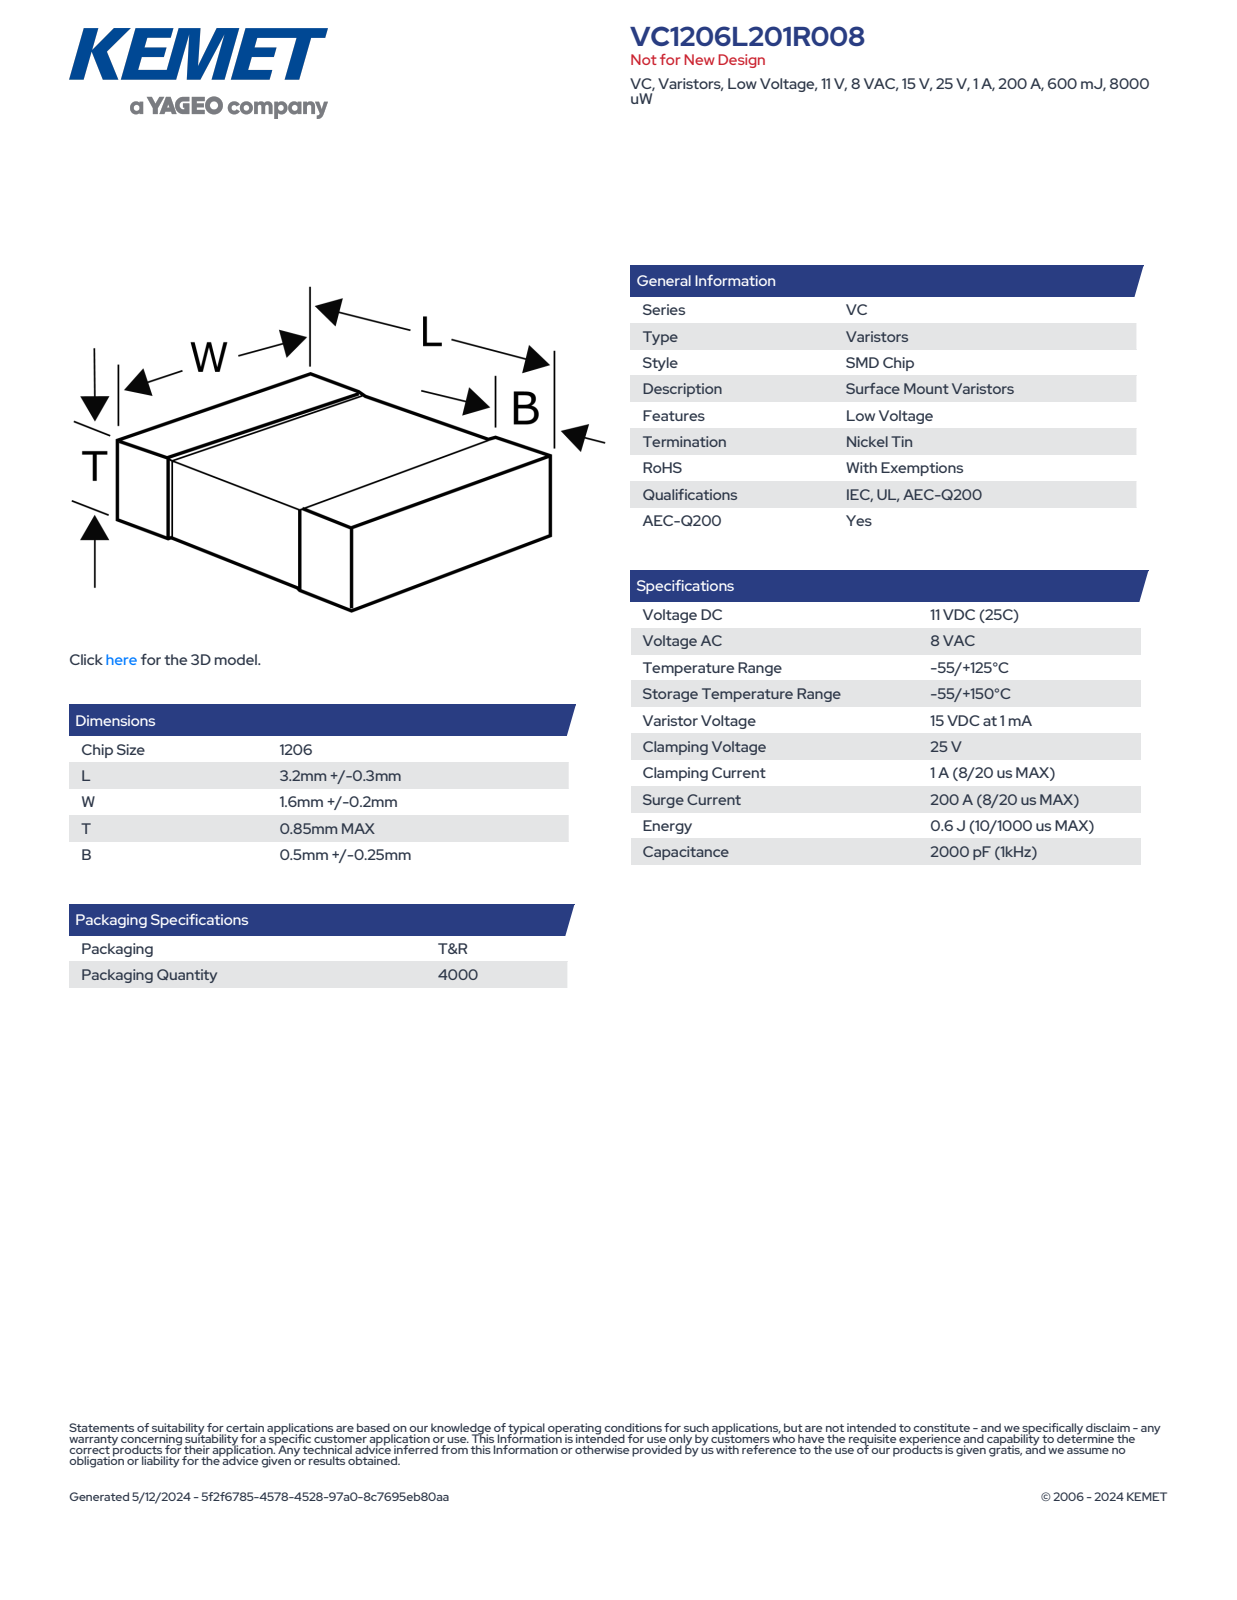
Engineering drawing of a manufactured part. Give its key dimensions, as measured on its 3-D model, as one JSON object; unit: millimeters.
{"part_name": "VS_SMD_1206_L3.50W1.8T0.85B0.75", "step_written_by": "SolidWorks 2014 (AUTOMOTIVE_DESIGN)", "units": "millimeters", "bodies": {"solids": 4, "faces": 125, "planar": 71, "cylindrical": 38, "other": 16}, "overall_size": [3.5, 1.8, 0.85], "volume_mm3": 5, "surface_area_mm2": 21, "face_to_face_distances": [0.81, 0.77, 0.85, 1.76, 1.72, 3.5, 1.8, 0.82, 0.78, 1.63]}
